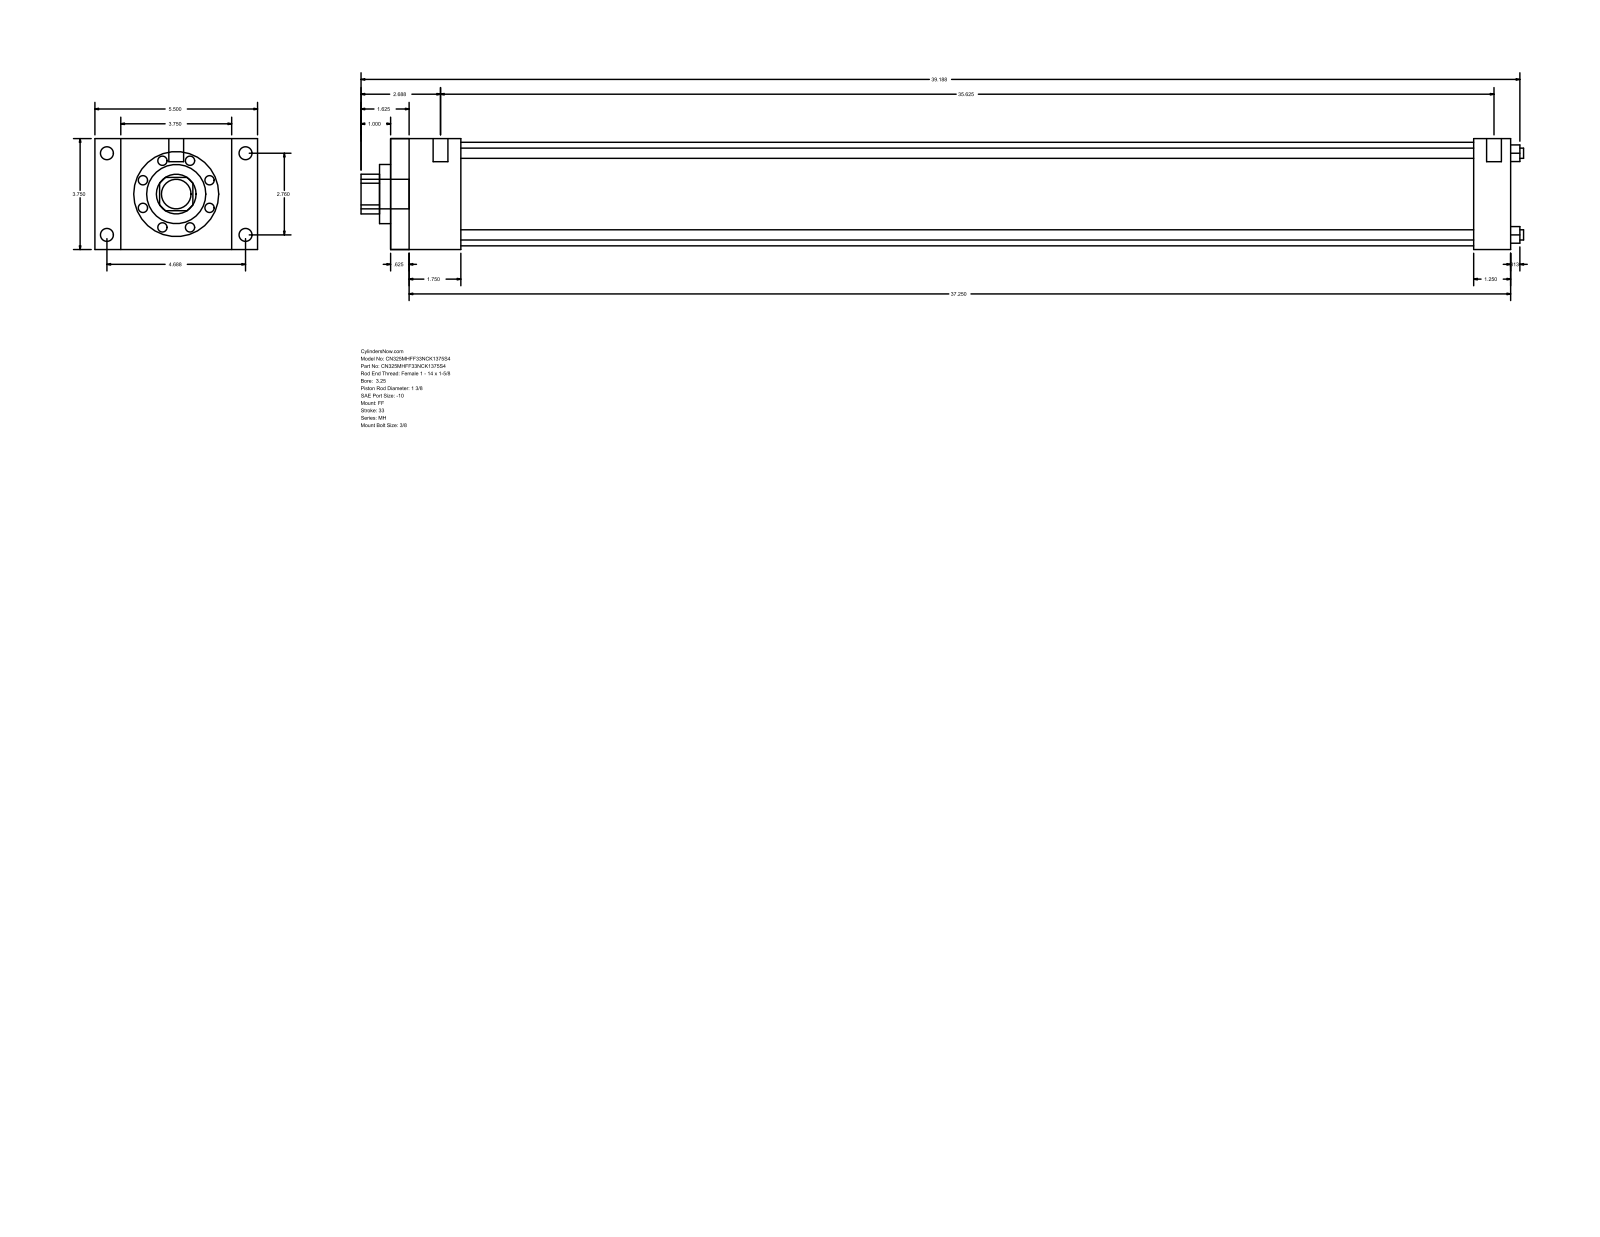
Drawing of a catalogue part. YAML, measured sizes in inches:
part_name: "MH_FF__0325_1.375"
step_written_by: "GSSL Pune (CONFIG_CONTROL_DESIGN)"
units: inches
bodies: {solids: 0, faces: 92, planar: 64, cylindrical: 28, other: 0}
overall_size: [39.313, 5.5, 3.75]
round_holes:
  - {diameter: 0.345, count: 4}
  - {diameter: 1.375, count: 1}
  - {diameter: 2, count: 1}
  - {diameter: 3.5, count: 1}
round_bosses_or_shafts:
  - {diameter: 0.438, count: 4}
  - {diameter: 0.219, count: 4}
  - {diameter: 0.5, count: 2}
  - {diameter: 1, count: 1}
partial_cylinders:
  - {radius: 0.672, count: 1}
face_to_face_distances: [3.75, 37.875, 0.625, 37.25, 0.875, 4.625, 36.625, 36, 1.25, 2.375]
hole_center_spacings: [1.952, 2.76, 3.903]
